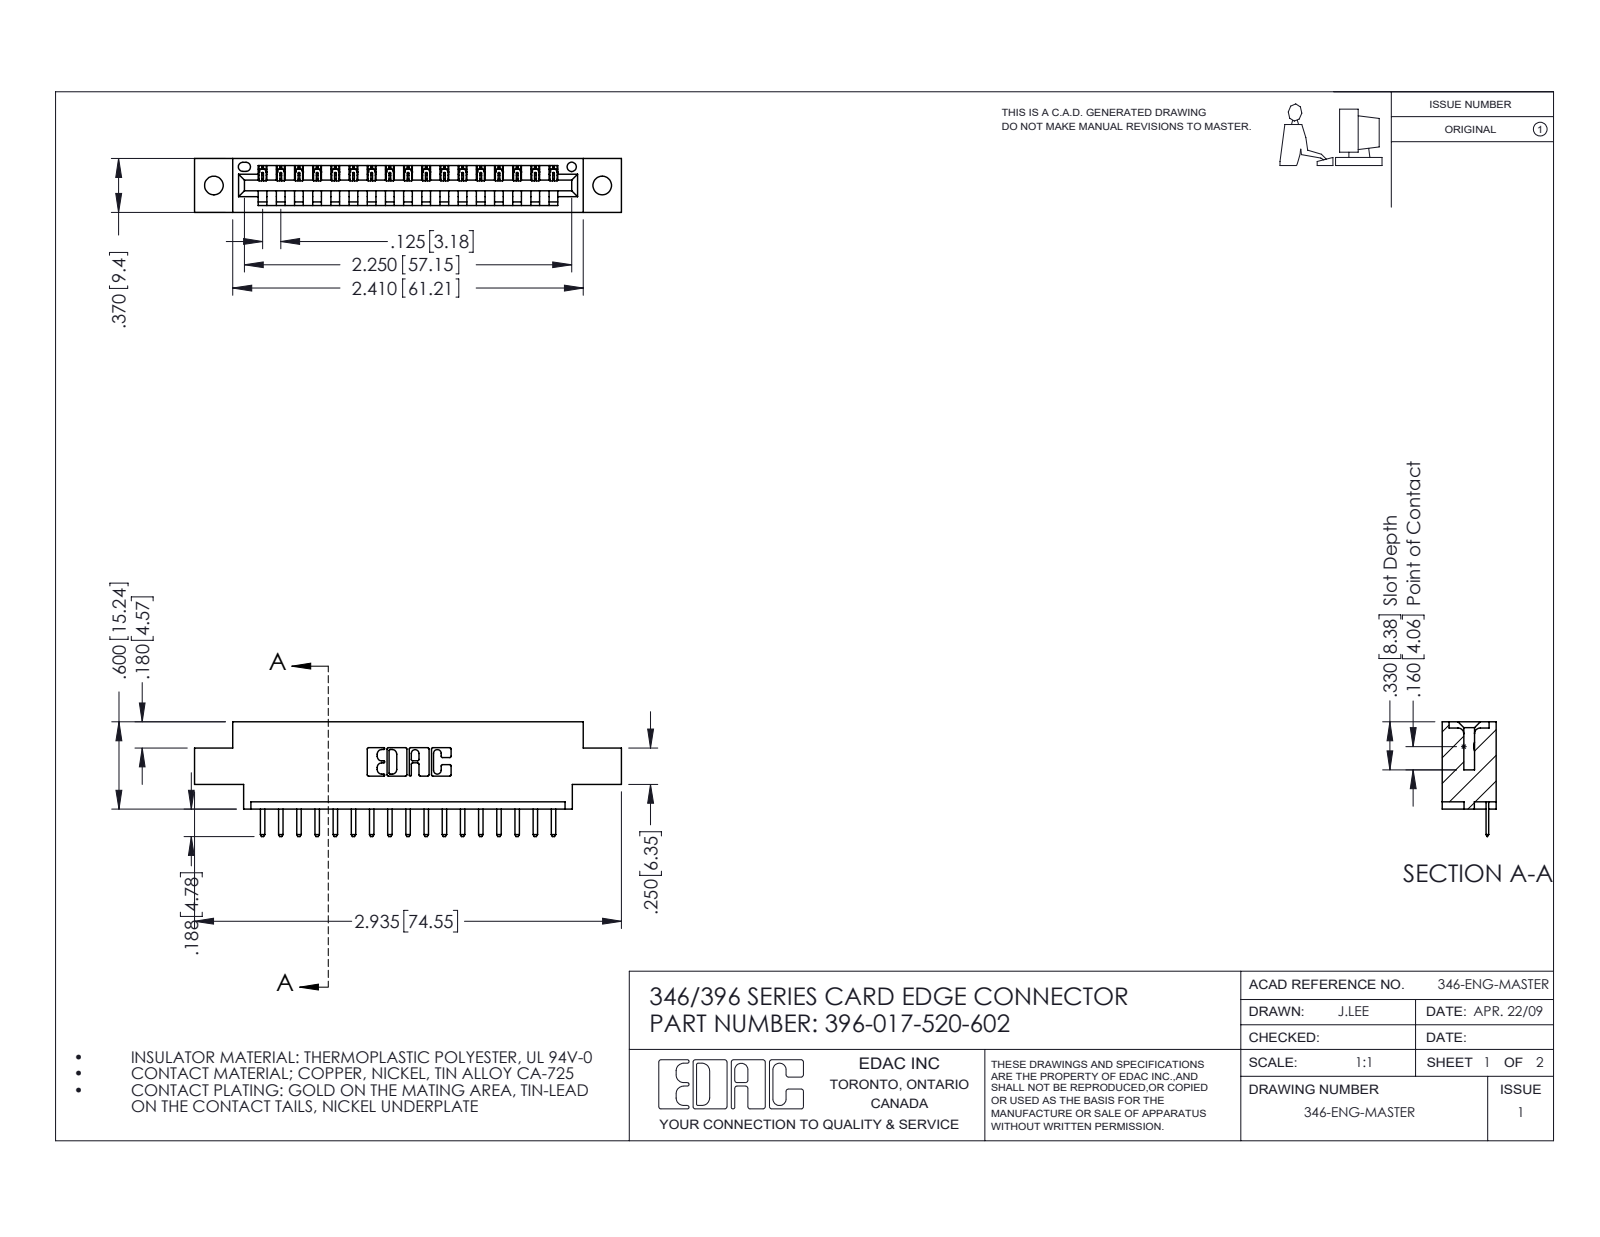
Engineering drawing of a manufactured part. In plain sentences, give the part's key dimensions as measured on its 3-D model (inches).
The part is named "346 Part_0.170 Offset - 0.128 Dia; 345-292-001_345-293-120; 396-017-520-602". Its 3-D file was written by "SolidWorks 2016 (CONFIG_CONTROL_DESIGN)". It is 18 solids with 1180 faces: 794 planar, 386 cylindrical and 0 other. Overall it measures 2.935 by 0.788 by 0.37 inches. Its volume is 0.41 cubic inches and its surface area 12.18 square inches. Round holes: 2 of diameter 0.128, 1 of diameter 0.064. Partial cylindrical surfaces (rounded edges, fillets, slot ends): 36 of radius 0.01, 34 of radius 0.006, 22 of radius 0.01, 6 of radius 0.007, 6 of radius 0.031, 3 of radius 0.026, 2 of radius 0.031, 2 of radius 0.04. The main face-to-face distances are 0.37, 0.048, 0.322, 0.25, 0.148, 0.222, 0.1, 0.174, 0.072, 0.298. The hole center spacings are 0.246, 2.463, 2.67.
